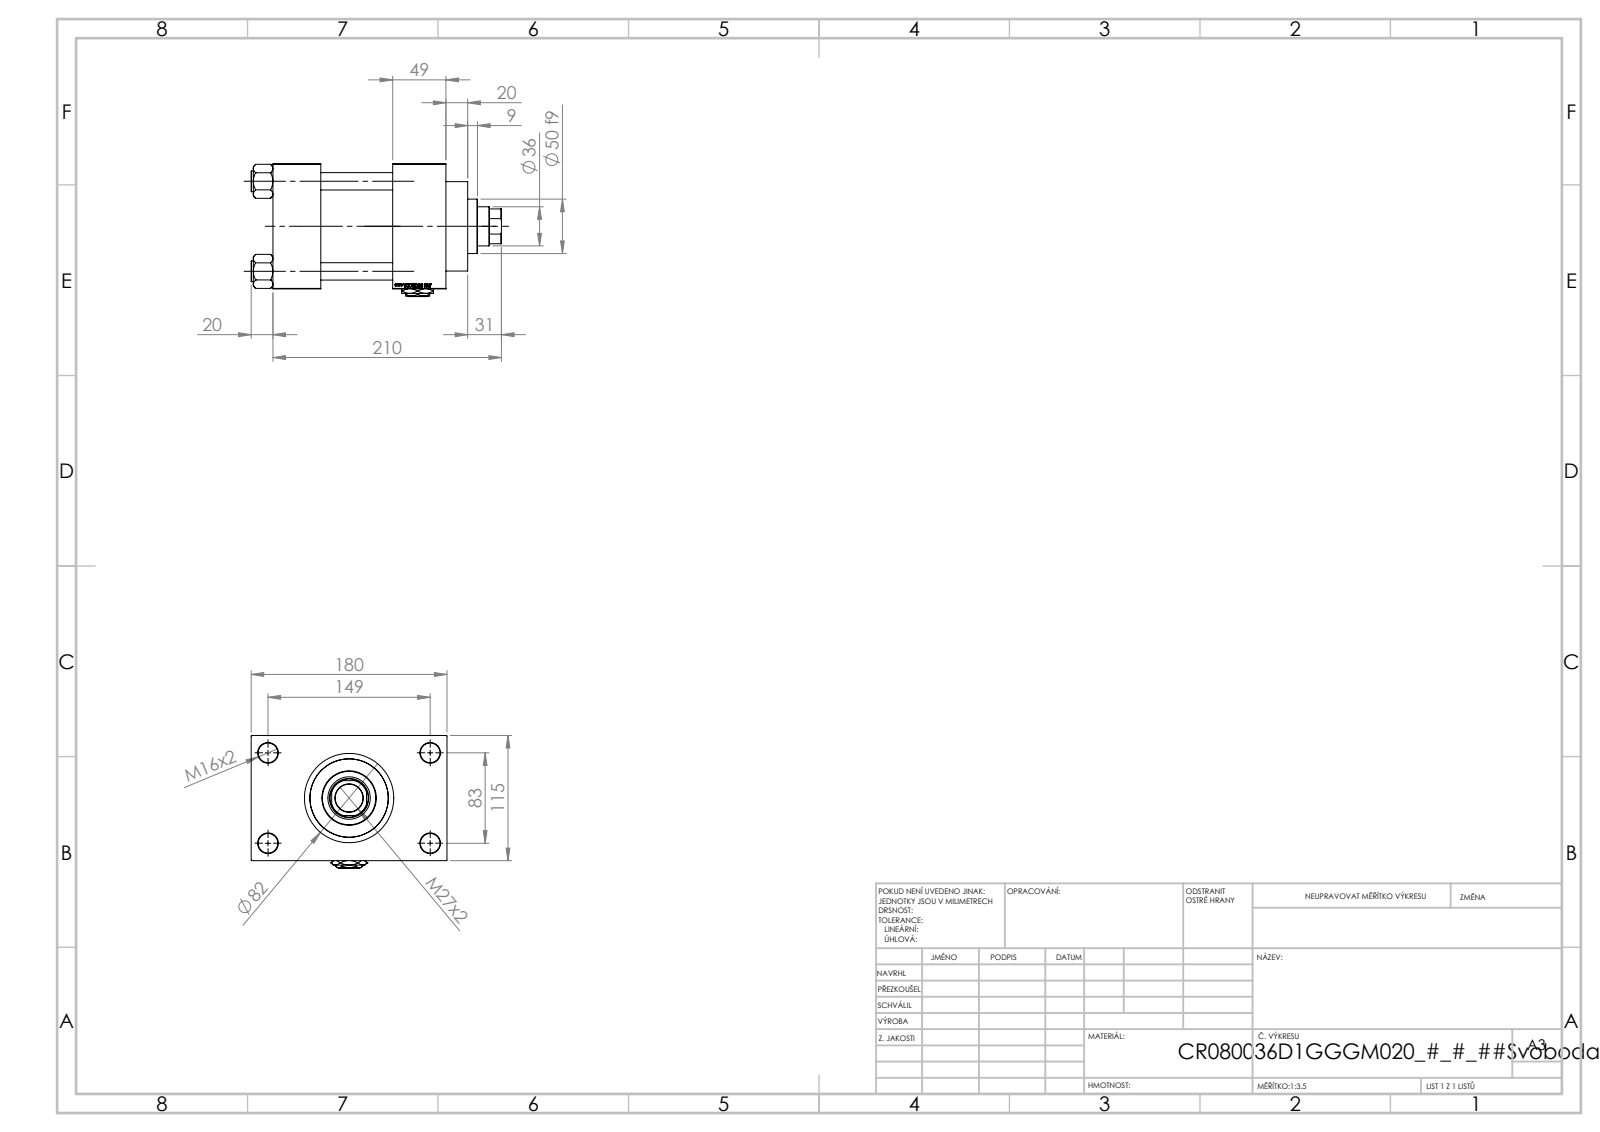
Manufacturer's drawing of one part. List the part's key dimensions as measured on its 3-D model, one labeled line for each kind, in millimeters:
Part name (STEP PRODUCT): NUT_M5_D; V215CR_D_TYCINKA; V215CR_D_Body; V215CR_VCP_D (+2 more)
STEP written by: SolidWorks 2019 (CONFIG_CONTROL_DESIGN)
Units: millimetres
Bodies: 12 solids, 1200 faces (569 planar, 93 cylindrical, 538 other)
Overall size (bounding box): 230 × 180 × 122
Volume: 1 987 000 mm³ · Surface area: 296 828 mm²
Round holes (diameter × count): ⌀16 ×4, ⌀18 ×4, ⌀7 ×2, ⌀26.44 ×2, ⌀35 ×2, ⌀25.5 ×1, ⌀36 ×1, ⌀39 ×1, ⌀61 ×1, ⌀72 ×1, ⌀80 ×1
Round bosses / shafts (diameter × count): ⌀19 ×4, ⌀86 ×1, ⌀82 ×1, ⌀50 ×1
Partial cylindrical surfaces — rounded edges, fillets, slot ends (radius × count): R17.5 ×1
Main face-to-face distances: 115, 66, 110, 49, 44, 159, 147.5, 32.5, 20, 69
Hole centre spacings: 33.15, 58.48, 82.7, 85.28, 89.24, 115.85, 142.43, 83
